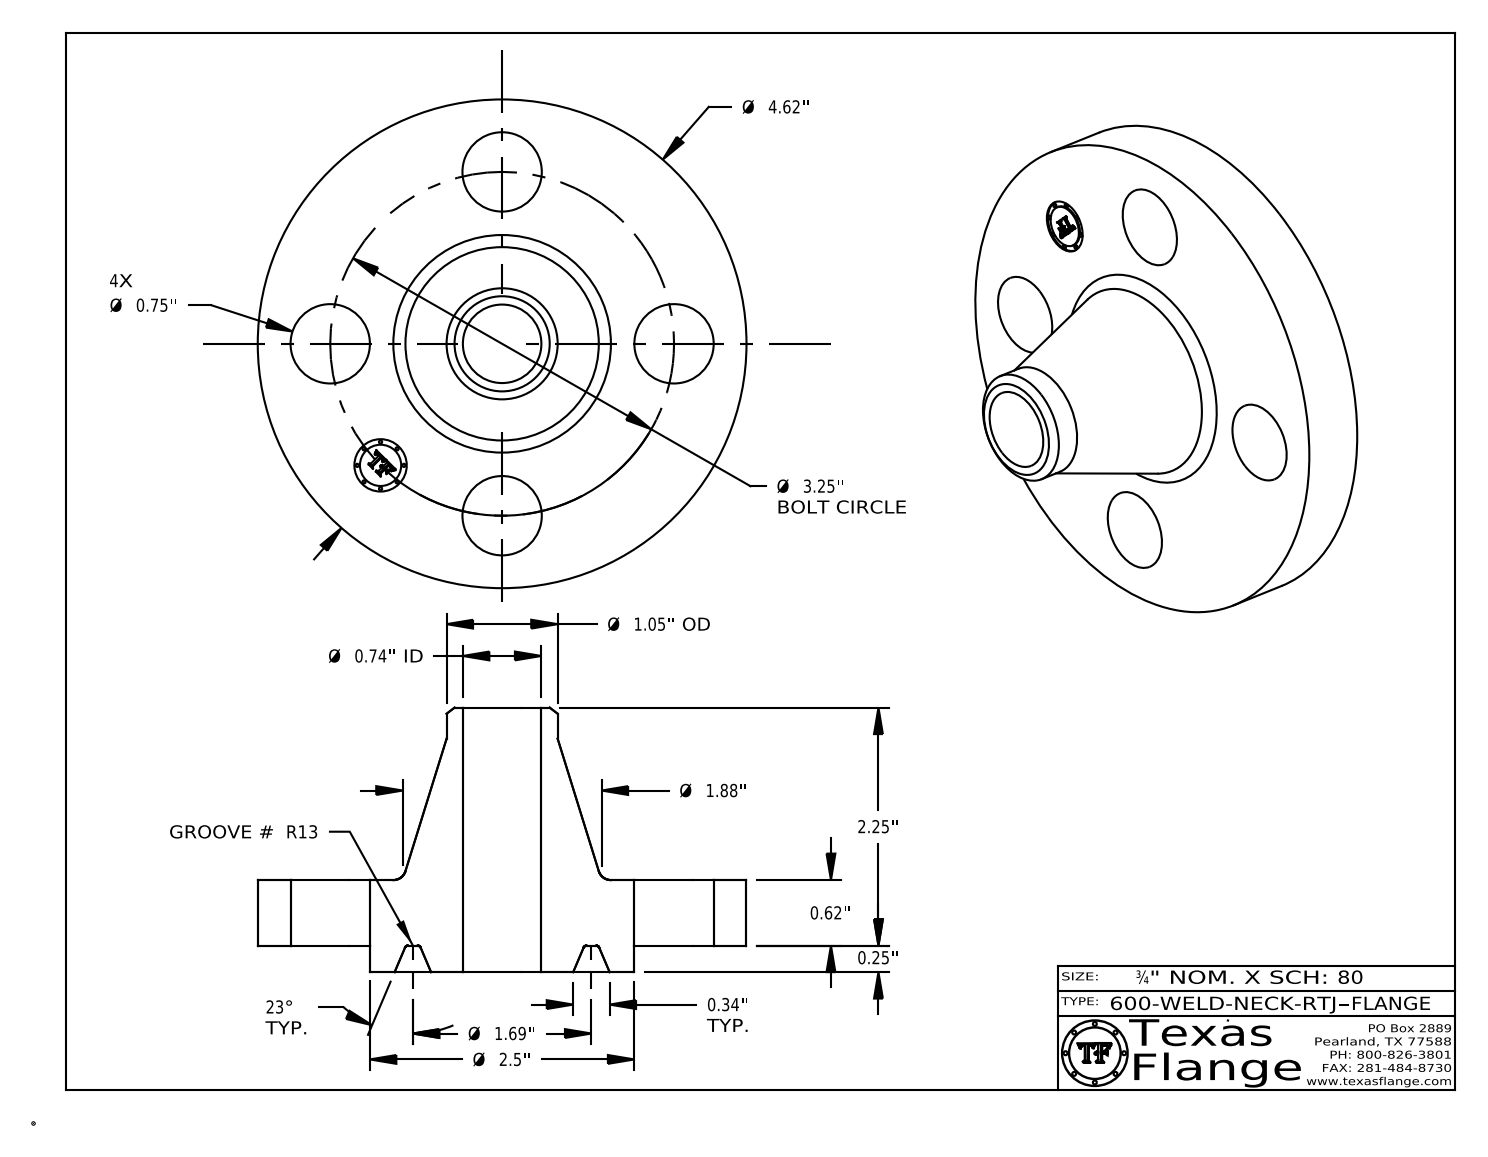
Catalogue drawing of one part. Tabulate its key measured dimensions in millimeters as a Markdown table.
| quantity | value |
| --- | --- |
| part name | 600-WELD-NECK-RTJ |
| STEP written by | CATIA V5 STEP AP214 (AUTOMOTIVE_DESIGN) |
| units | millimeters |
| bodies | 1 solid, 421 faces (371 planar, 36 cylindrical, 14 other) |
| overall size | 117.3 × 117.3 × 63.5 |
| volume | 191 700 mm³ |
| surface area | 37 930 mm² |
| round holes (diameter × count) | 19.1 × 4, 12.6 × 1, 18.8 × 1 |
| round bosses / shafts (diameter × count) | 0.8 × 8, 117.3 × 1, 63.5 × 1, 26.7 × 1, 9.9 × 1 |
| main face-to-face distances | 15.7, 6.4, 22.1, 63.5, 57.2, 41.4, 21.7, 15.4, 0.4, 41.8 |
| hole center spacings | 41.3, 58.4, 31.6, 76.3, 82.6 |
